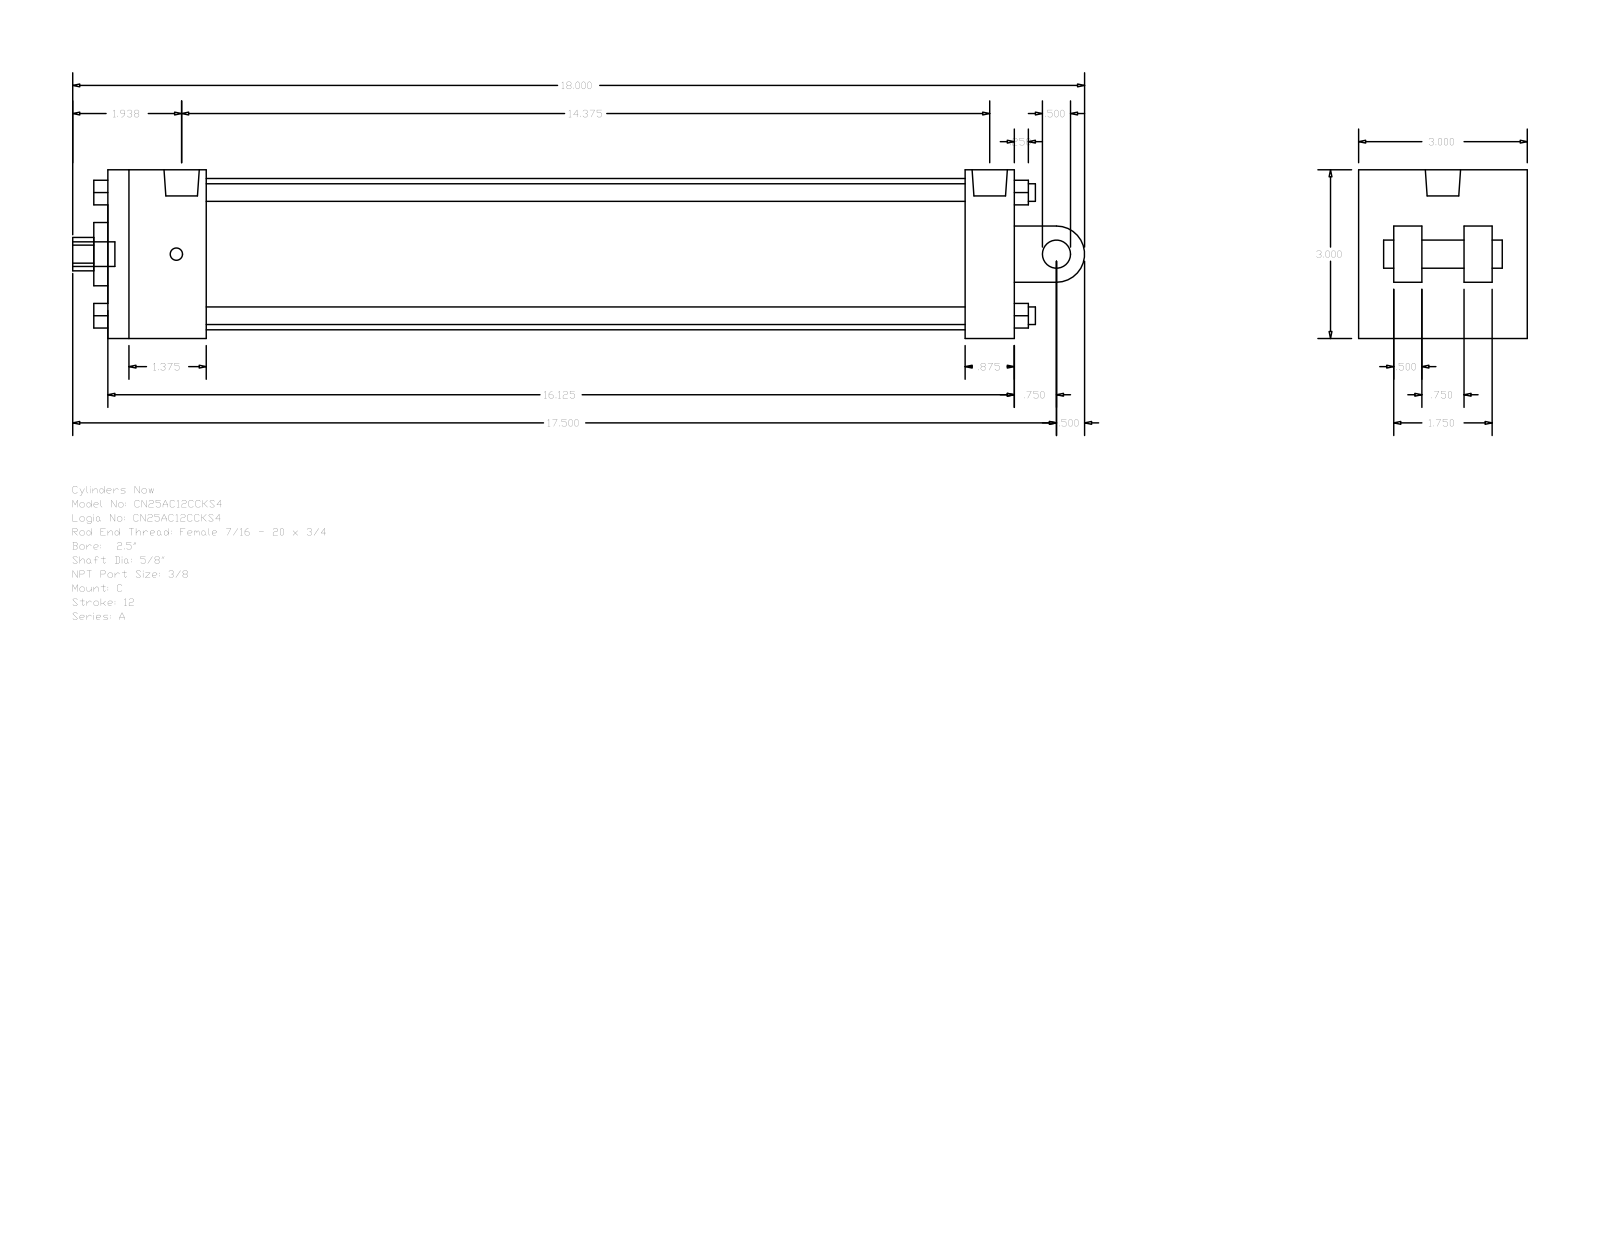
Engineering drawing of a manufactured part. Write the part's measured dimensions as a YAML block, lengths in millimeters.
part_name: "A_C__0250_0.625"
step_written_by: "GSSL Pune (CONFIG_CONTROL_DESIGN)"
units: millimeters
bodies: {solids: 0, faces: 135, planar: 102, cylindrical: 33, other: 0}
overall_size: [457.2, 76.2, 76.2]
round_holes:
  - {diameter: 5.56, count: 2}
  - {diameter: 15.88, count: 1}
  - {diameter: 15.93, count: 1}
  - {diameter: 28.57, count: 1}
  - {diameter: 68.33, count: 1}
round_bosses_or_shafts:
  - {diameter: 7.94, count: 4}
  - {diameter: 5.56, count: 2}
  - {diameter: 15.93, count: 1}
  - {diameter: 12.7, count: 1}
  - {diameter: 11.11, count: 1}
partial_cylinders:
  - {radius: 7.54, count: 1}
  - {radius: 12.7, count: 1}
face_to_face_distances: [76.2, 409.57, 44.45, 387.35, 342.9, 365.12, 22.22, 50.8, 12.7, 15.87]
hole_center_spacings: [2.38]
